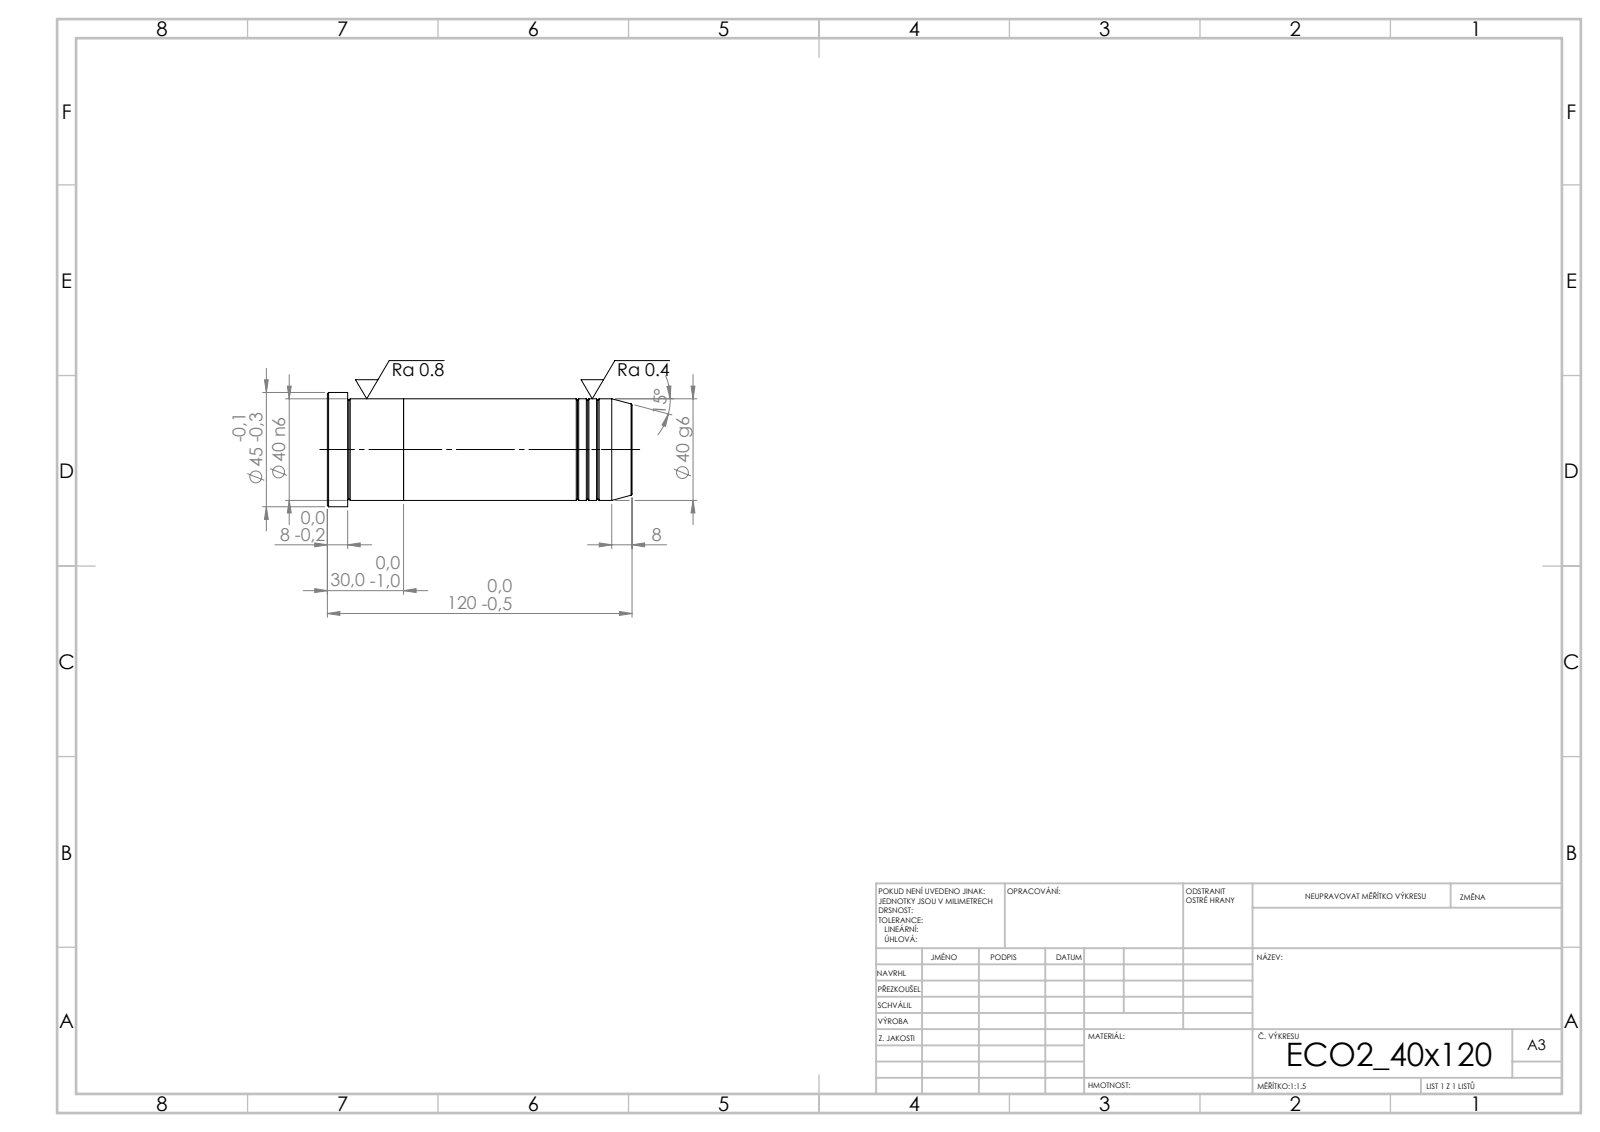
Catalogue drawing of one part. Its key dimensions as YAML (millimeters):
step_written_by: "SolidWorks 2019 (CONFIG_CONTROL_DESIGN)"
units: millimeters
bodies: {solids: 2, faces: 39, planar: 5, cylindrical: 12, other: 22}
overall_size: [120, 45, 45]
volume: 152212
surface_area: 20844
round_bosses_or_shafts:
  - {diameter: 45, count: 1}
  - {diameter: 40, count: 1}
face_to_face_distances: [30, 90, 120, 112, 22, 8]
